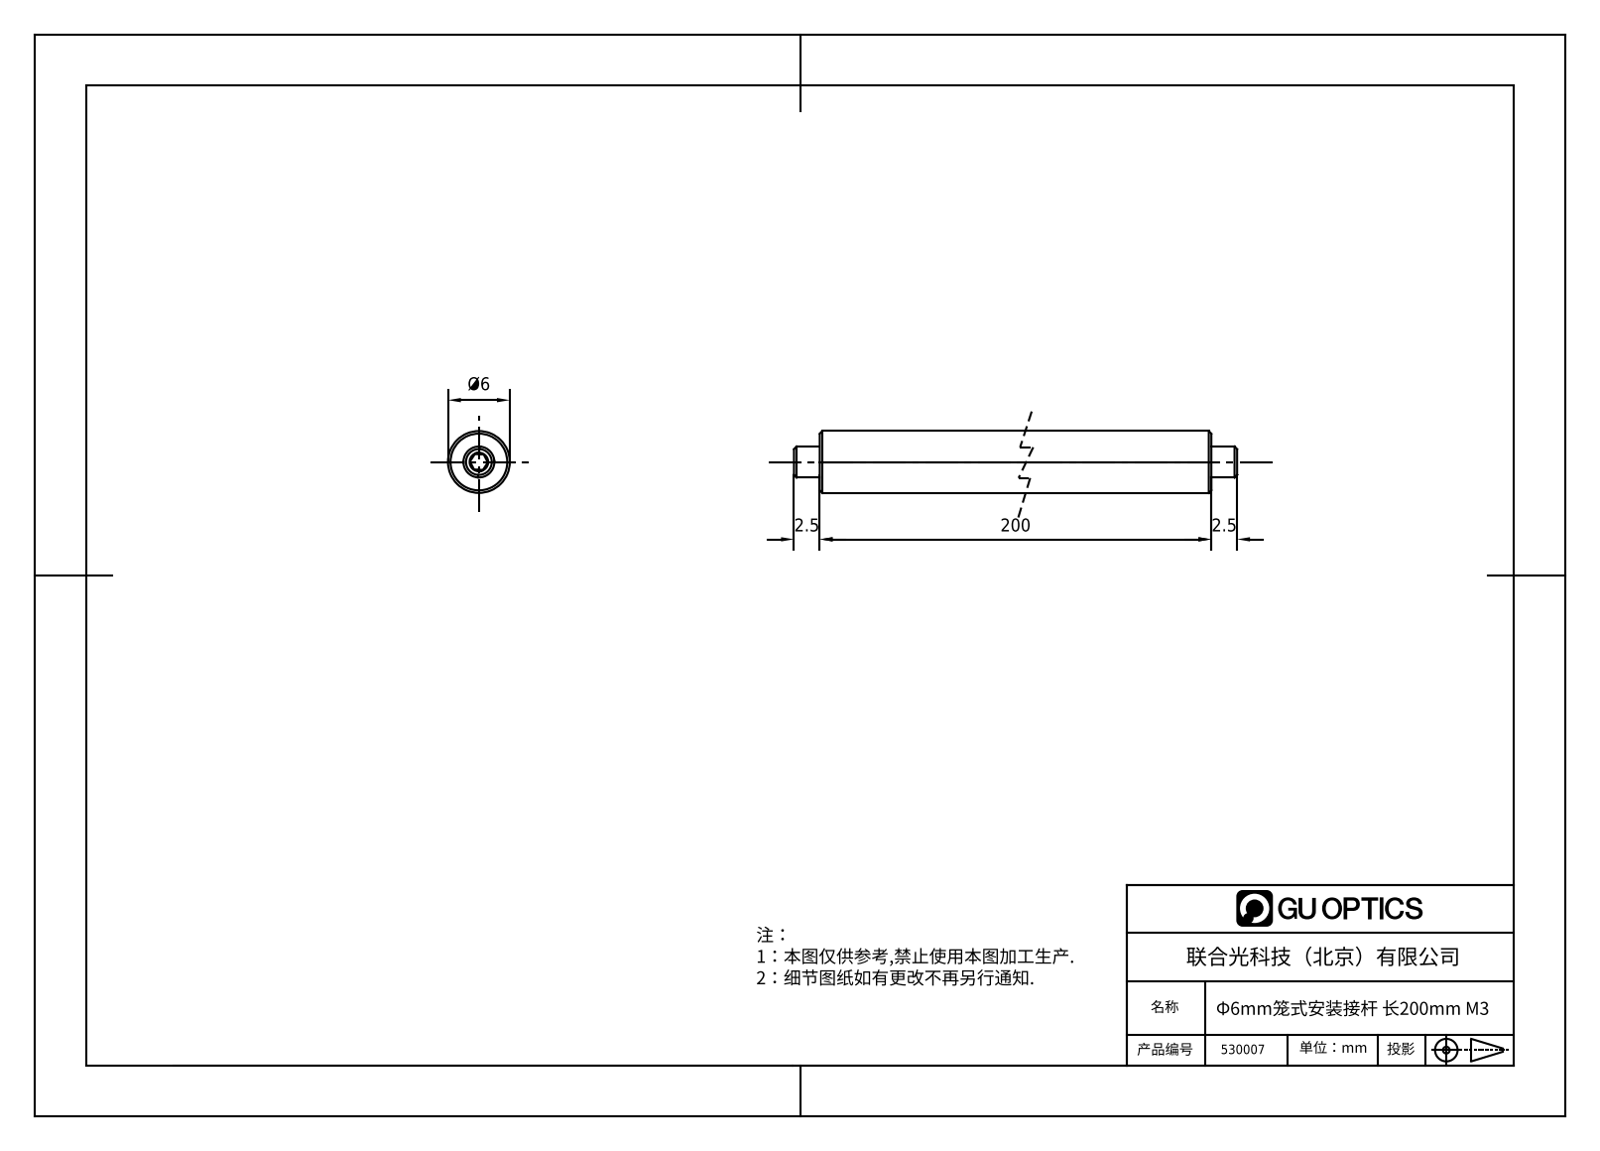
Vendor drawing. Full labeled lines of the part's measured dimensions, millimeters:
STEP written by: SolidWorks 2018 (AUTOMOTIVE_DESIGN)
Units: millimetres
Bodies: 0 solids, 36 faces (18 planar, 6 cylindrical, 12 other)
Overall size (bounding box): 205 × 6 × 6
Round bosses / shafts (diameter × count): ⌀6 ×1, ⌀3 ×1
Main face-to-face distances: 200, 1.5, 2.5, 202.5, 1, 204, 201.5, 205, 203
